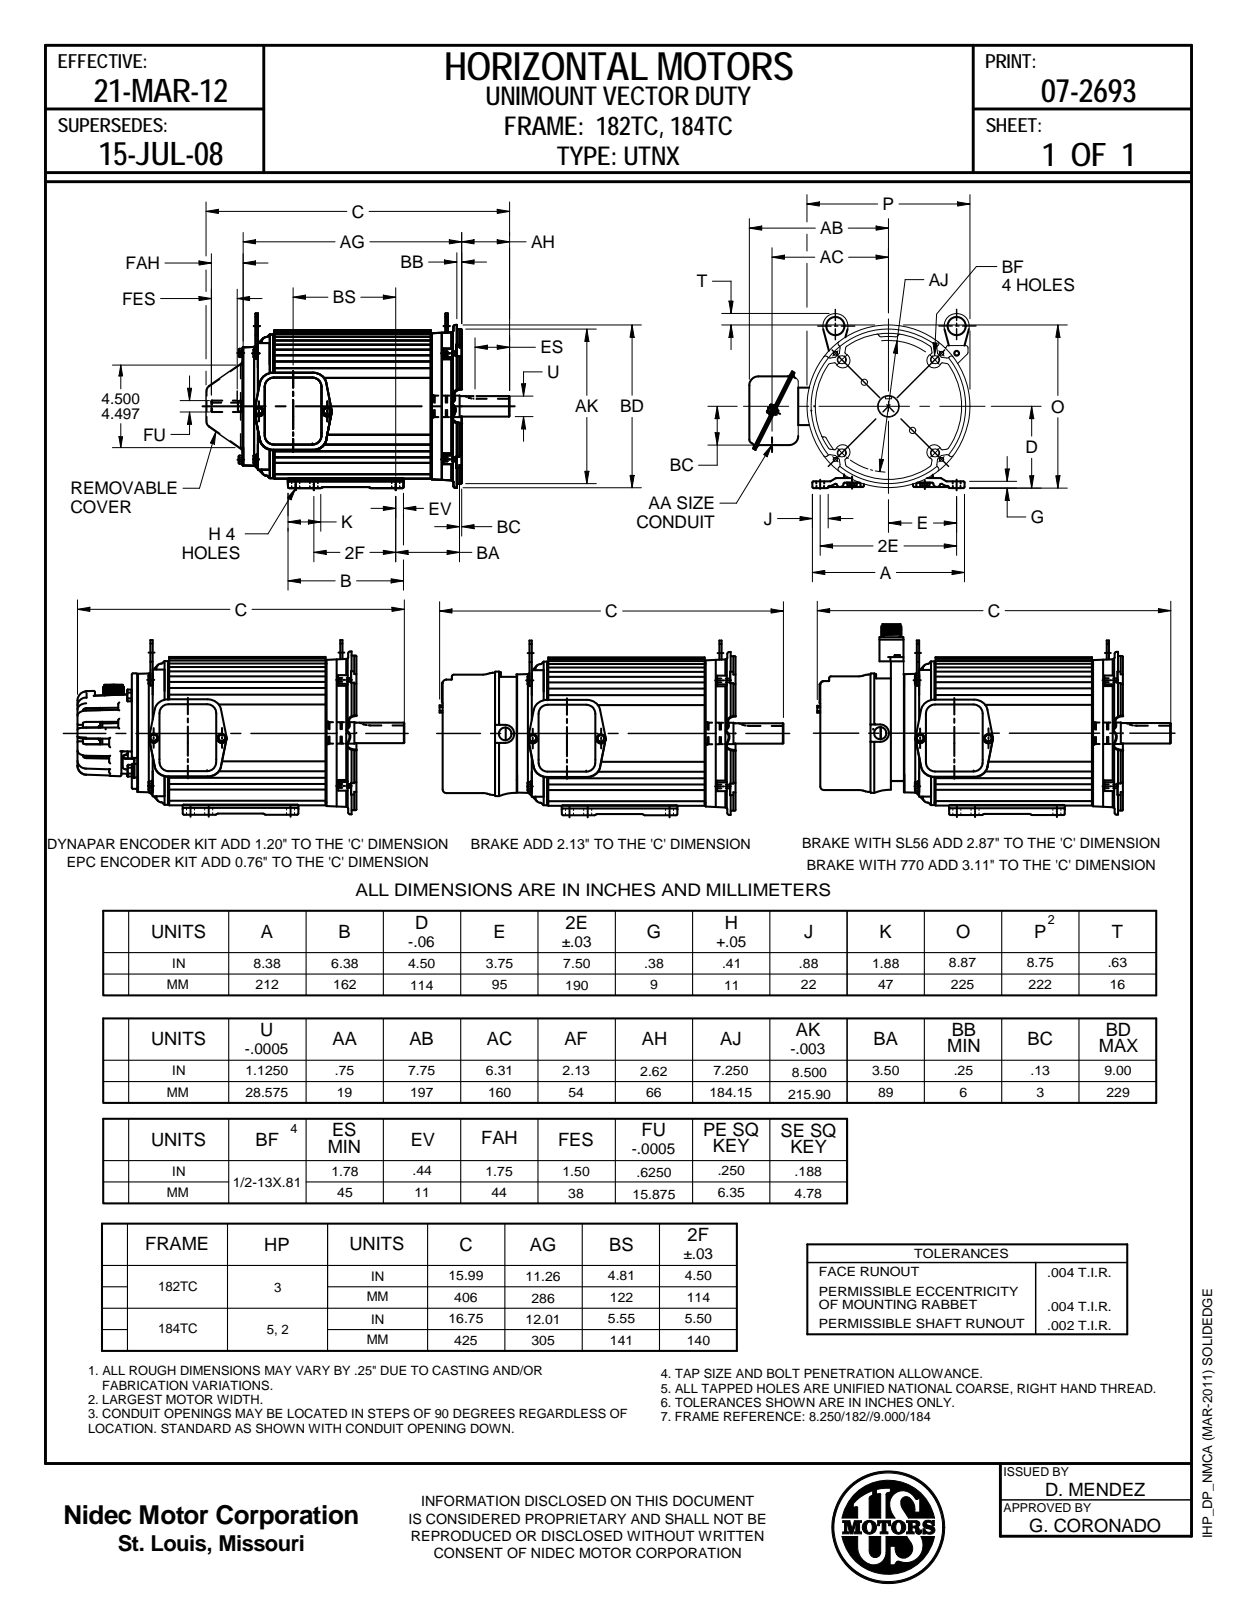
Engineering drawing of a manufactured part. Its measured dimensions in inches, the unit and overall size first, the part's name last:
Units: inches
Overall size (bounding box): 16.735 × 12.052 × 9.5
Round holes (diameter × count): ⌀0.234 ×4, ⌀0.277 ×4, ⌀0.406 ×4, ⌀0.232 ×2, ⌀0.266 ×2, ⌀0.281 ×2, ⌀1 ×2, ⌀0.174 ×1, ⌀1.12 ×1, ⌀1.191 ×1
Round bosses / shafts (diameter × count): ⌀0.328 ×2, ⌀8.5 ×1, ⌀8.315 ×1, ⌀7.64 ×1, ⌀6.5 ×1, ⌀4.5 ×1, ⌀1.18 ×1, ⌀1.179 ×1
Partial cylindrical surfaces — rounded edges, fillets, slot ends (radius × count): R0.063 ×142, R0.016 ×80, R0.031 ×74, R0.061 ×52, R0.094 ×20, R0.06 ×16, R0.5 ×14, R0.125 ×11
Main face-to-face distances: 10.798, 0.893, 11.691, 0.048, 0.18, 0.25, 0.312, 0.581, 11.379, 0.125
Hole centre spacings: 2.937, 3.76, 4.154, 1.5, 3.844, 4, 4.313, 5.064
Volume: 611.2 in³ · Surface area: 909.9 in²
Bodies: 5 solids, 2762 faces (614 planar, 751 cylindrical, 1397 other)
Part name (STEP PRODUCT): UN2T3BC
STEP written by: SolidWorks 2021 (AUTOMOTIVE_DESIGN)
